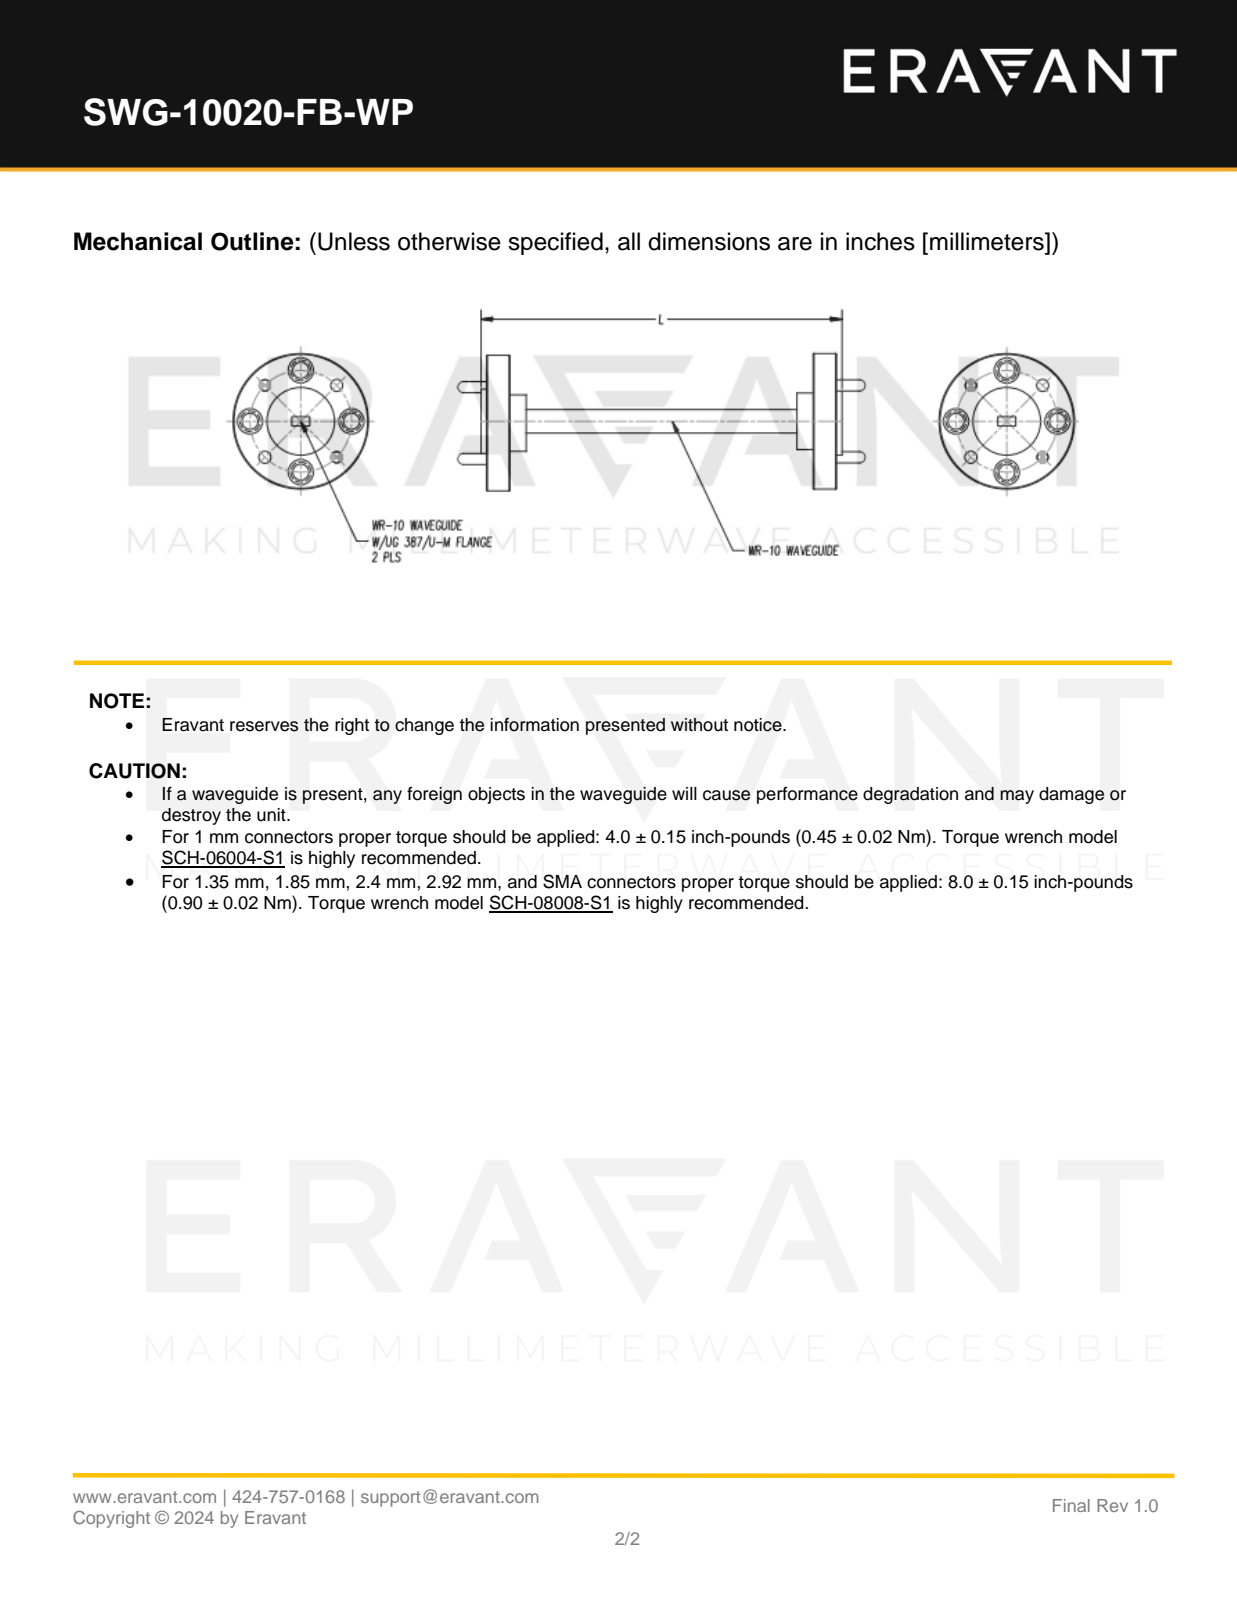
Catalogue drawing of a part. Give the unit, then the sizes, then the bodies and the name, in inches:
Units: inches
Overall size (bounding box): 2.305 × 0.75 × 0.75
Round holes (diameter × count): ⌀0.061 ×4, ⌀0.067 ×4, ⌀0.089 ×4, ⌀0.14 ×4
Round bosses / shafts (diameter × count): ⌀0.063 ×4, ⌀0.75 ×1, ⌀0.375 ×1, ⌀0.36 ×1
Main face-to-face distances: 0.13, 1.81, 0.04, 1.68, 0.09, 0.09, 0.05, 1.94, 0.04, 0.14
Hole centre spacings: 0.215, 0.398, 0.519, 0.562, 0.52, 0.563
Volume: 0.157 in³ · Surface area: 4.706 in²
Bodies: 5 solids, 140 faces (32 planar, 68 cylindrical, 40 other)
Part name (STEP PRODUCT): SWG-10020-FB
STEP written by: SolidWorks 2013 (CONFIG_CONTROL_DESIGN)
